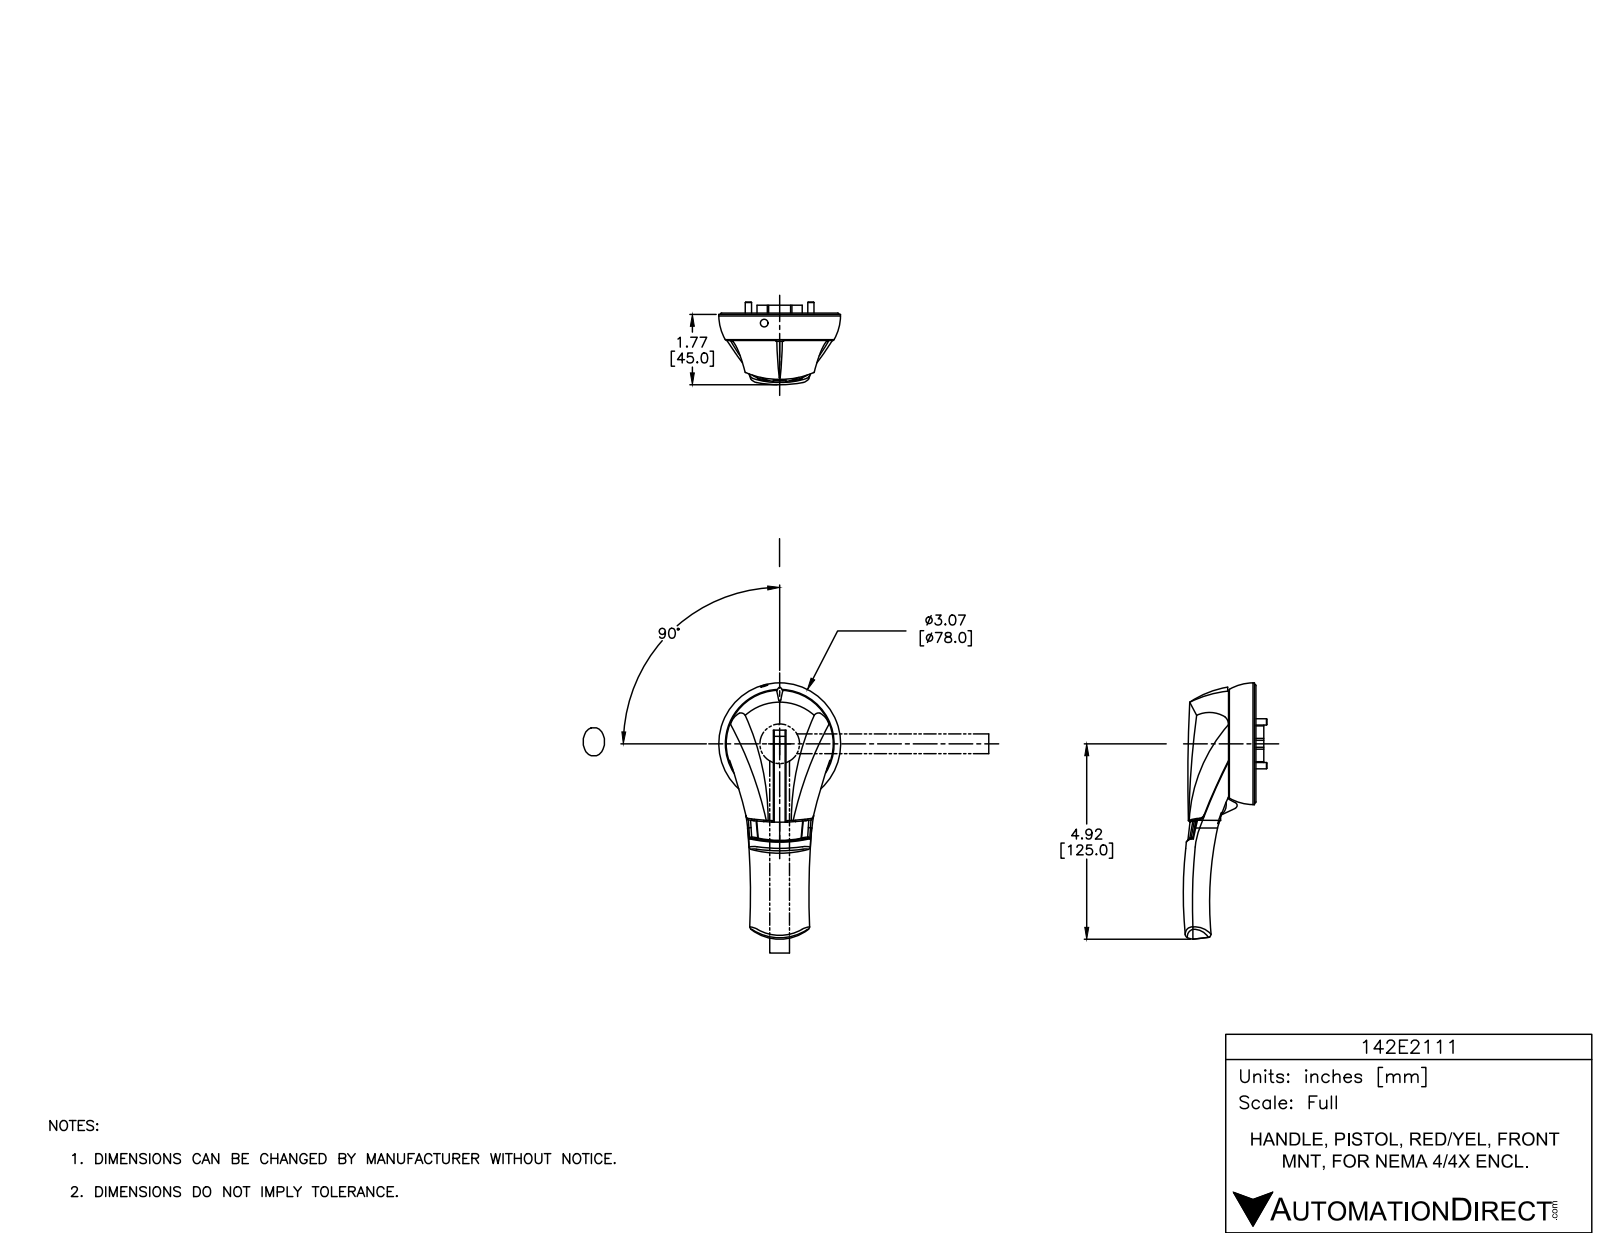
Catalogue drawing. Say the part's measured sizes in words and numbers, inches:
The part is named "142E2111". Its 3-D file was written by "SolidWorks 2015 (AUTOMOTIVE_DESIGN)". It is 8 solids with 1516 faces: 810 planar, 548 cylindrical and 158 other. Overall it measures 6.458 by 3.07 by 2.079 inches. Its volume is 9.514 cubic inches and its surface area 87.32 square inches. Round holes: 6 of diameter 0.157, 4 of diameter 0.339, 4 of diameter 0.425, 3 of diameter 0.03, 2 of diameter 0.169, 2 of diameter 0.362, 1 of diameter 0.118, 1 of diameter 0.189, 1 of diameter 2.992. Round bosses or shafts: 11 of diameter 0.02, 4 of diameter 0.335, 4 of diameter 0.315, 3 of diameter 0.089, 3 of diameter 0.069, 2 of diameter 0.228, 1 of diameter 2.819, 1 of diameter 2.701. Partial cylindrical surfaces (rounded edges, fillets, slot ends): 221 of radius 0.01, 20 of radius 0.015, 20 of radius 0.034, 15 of radius 0.03, 4 of radius 0.039, 3 of radius 0.025, 3 of radius 5.437, 2 of radius 0.079. The main face-to-face distances are 0.024, 0.701, 0.713, 0.689, 0.035, 0.102, 0.276, 0.173, 0.244, 0.047. The hole center spacings are 0.961, 0.309, 0.669, 1.098, 1.102, 1.203, 1.575, 1.881.
